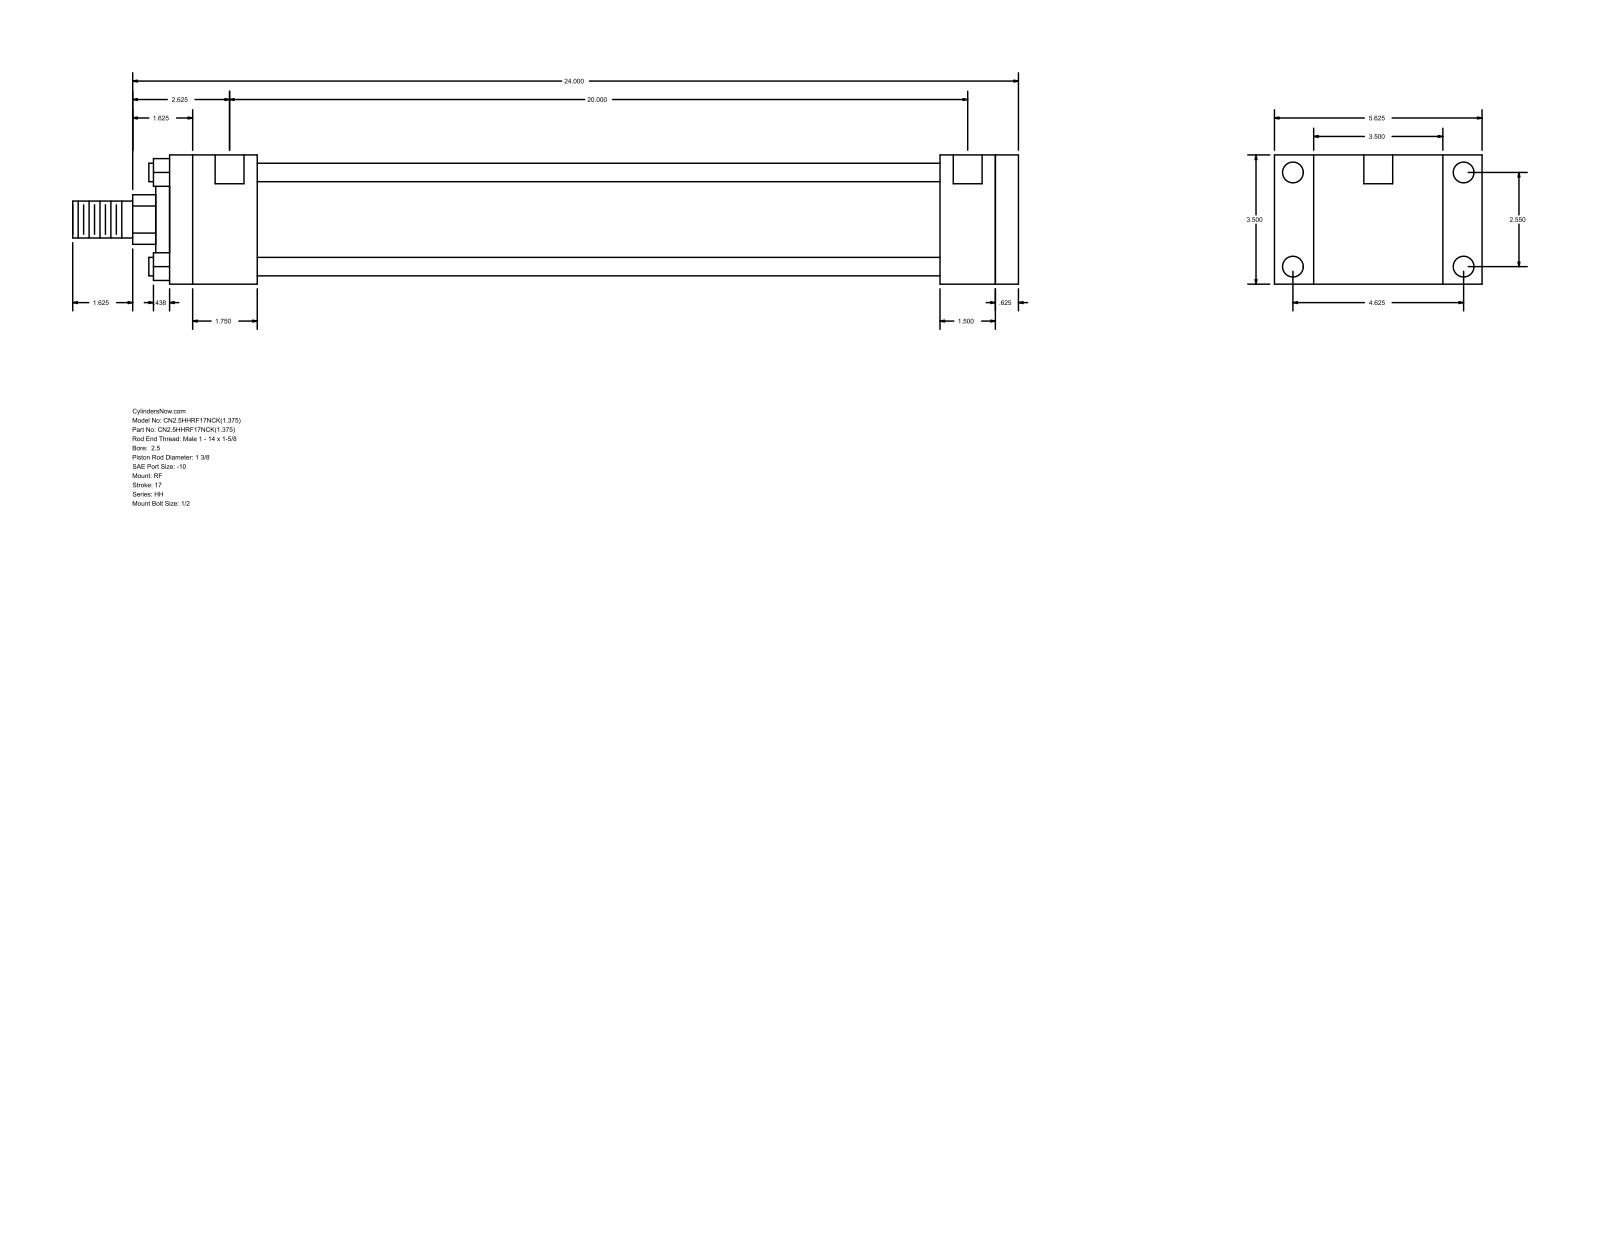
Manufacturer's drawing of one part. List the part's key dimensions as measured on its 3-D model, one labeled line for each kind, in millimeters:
Part name (STEP PRODUCT): HH_RF__0250_1.375
STEP written by: GSSL Pune (CONFIG_CONTROL_DESIGN)
Units: millimetres
Bodies: 0 solids, 92 faces (64 planar, 28 cylindrical, 0 other)
Overall size (bounding box): 650.88 × 142.88 × 88.9
Round holes (diameter × count): ⌀5.56 ×4, ⌀14.3 ×4, ⌀19.84 ×2
Round bosses / shafts (diameter × count): ⌀12.7 ×4, ⌀73.03 ×1, ⌀50.8 ×1, ⌀34.92 ×1, ⌀25.4 ×1
Partial cylindrical surfaces — rounded edges, fillets, slot ends (radius × count): R17.06 ×1
Main face-to-face distances: 88.9, 584.2, 568.33, 15.87, 60.32, 508.01, 523.88, 530.22, 469.9, 38.11
Hole centre spacings: 64.76, 117.48, 134.15, 511.17, 1.58, 1.59, 508, 509.58
